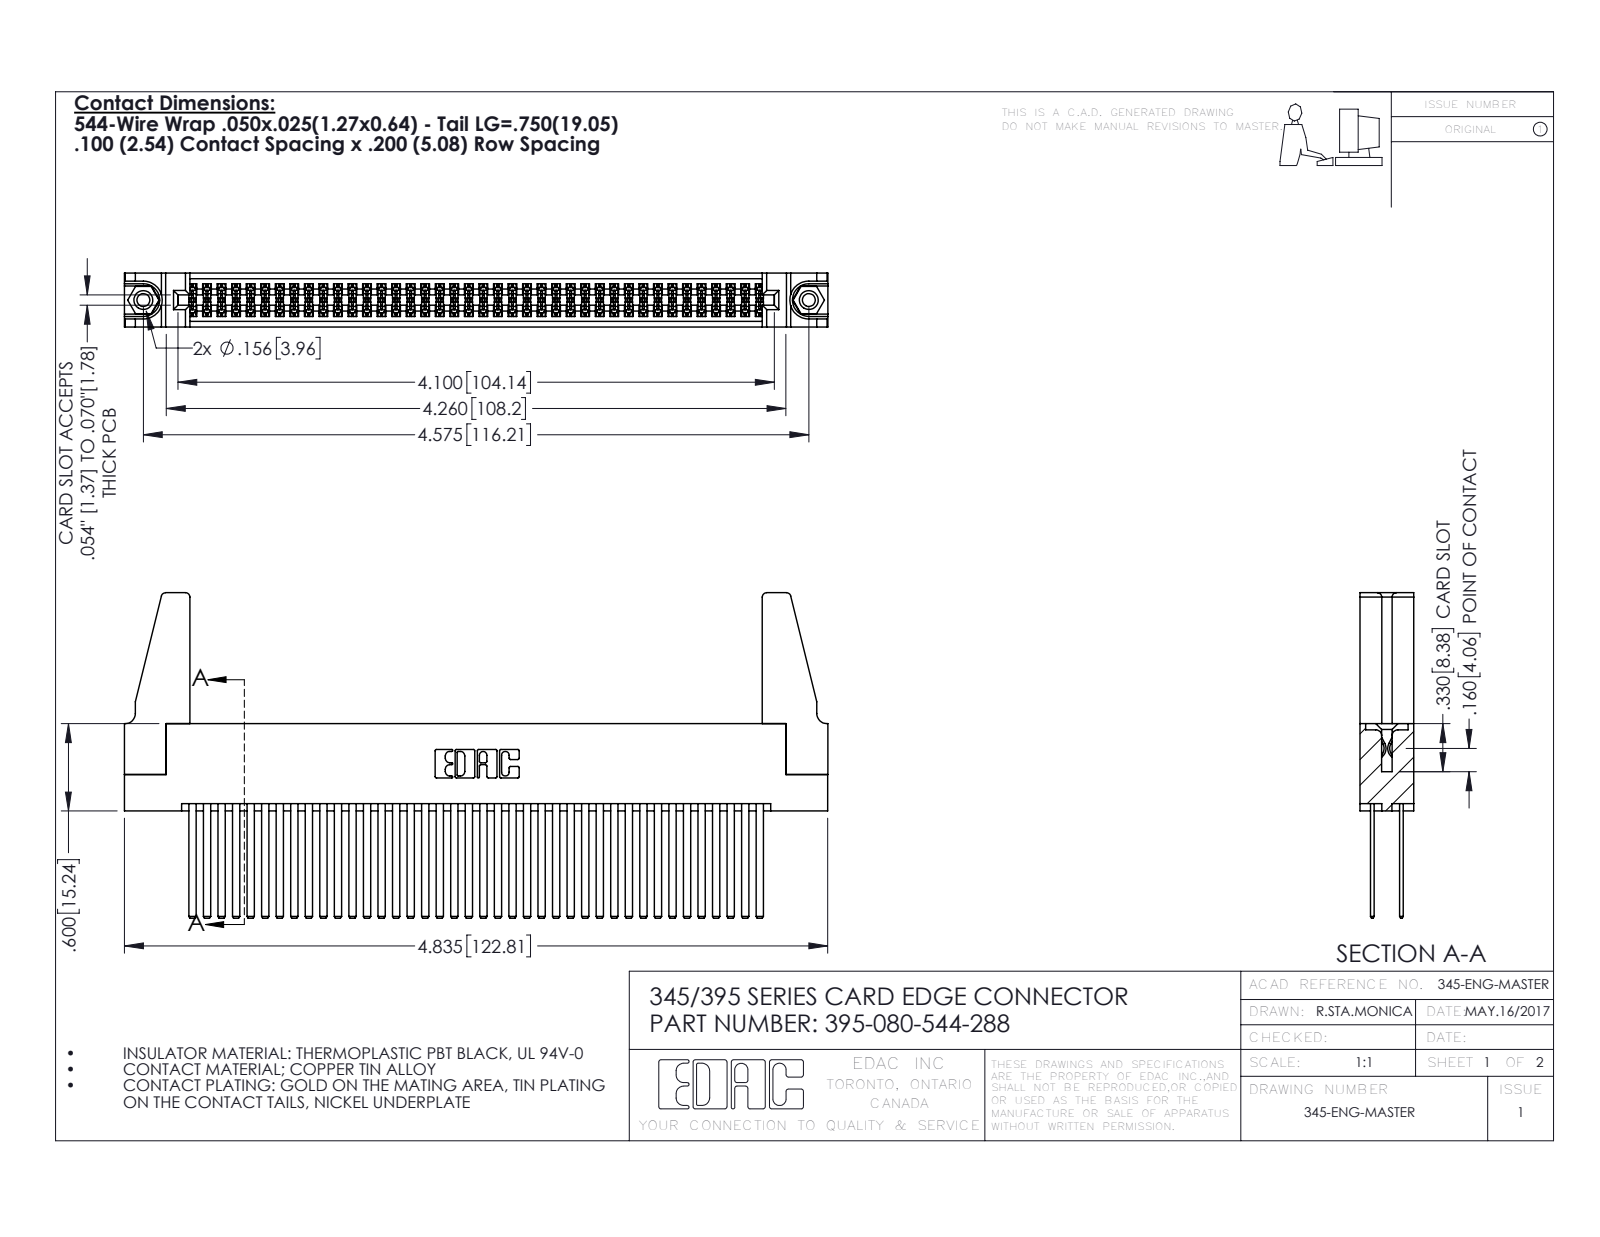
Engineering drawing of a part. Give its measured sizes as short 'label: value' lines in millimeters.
name: 345-220-078_345-220-088; 345-250-001_345-250-001-102; 345-292-001_345-293-144; 345 Part_Flush Mounting Lugs - 0.156 Dia-TH (+1 more)
written by: SolidWorks 2016 (CONFIG_CONTROL_DESIGN)
unit: mm
bodies: 85 solids, 3770 faces (2472 planar, 1282 cylindrical, 16 other)
size: 122.8 × 56.8 × 9.4
volume: 16 300 mm³; area: 25 640 mm²
holes: 2× ⌀2.3, 2× ⌀3.2, 2× ⌀4, 1× ⌀1.6
bosses: 2× ⌀3.9
rounds: 120× R0.2, 22× R0.3, 8× R0.8, 6× R0.2, 6× R0.8, 3× R0.7, 2× R0.4, 2× R0.5
face distances: 1.8, 7.6, 5.1, 2.5, 6.9, 0.6, 5.7, 9.4, 4.4, 3.8
hole spacings: 6.9, 110.2, 116.2
